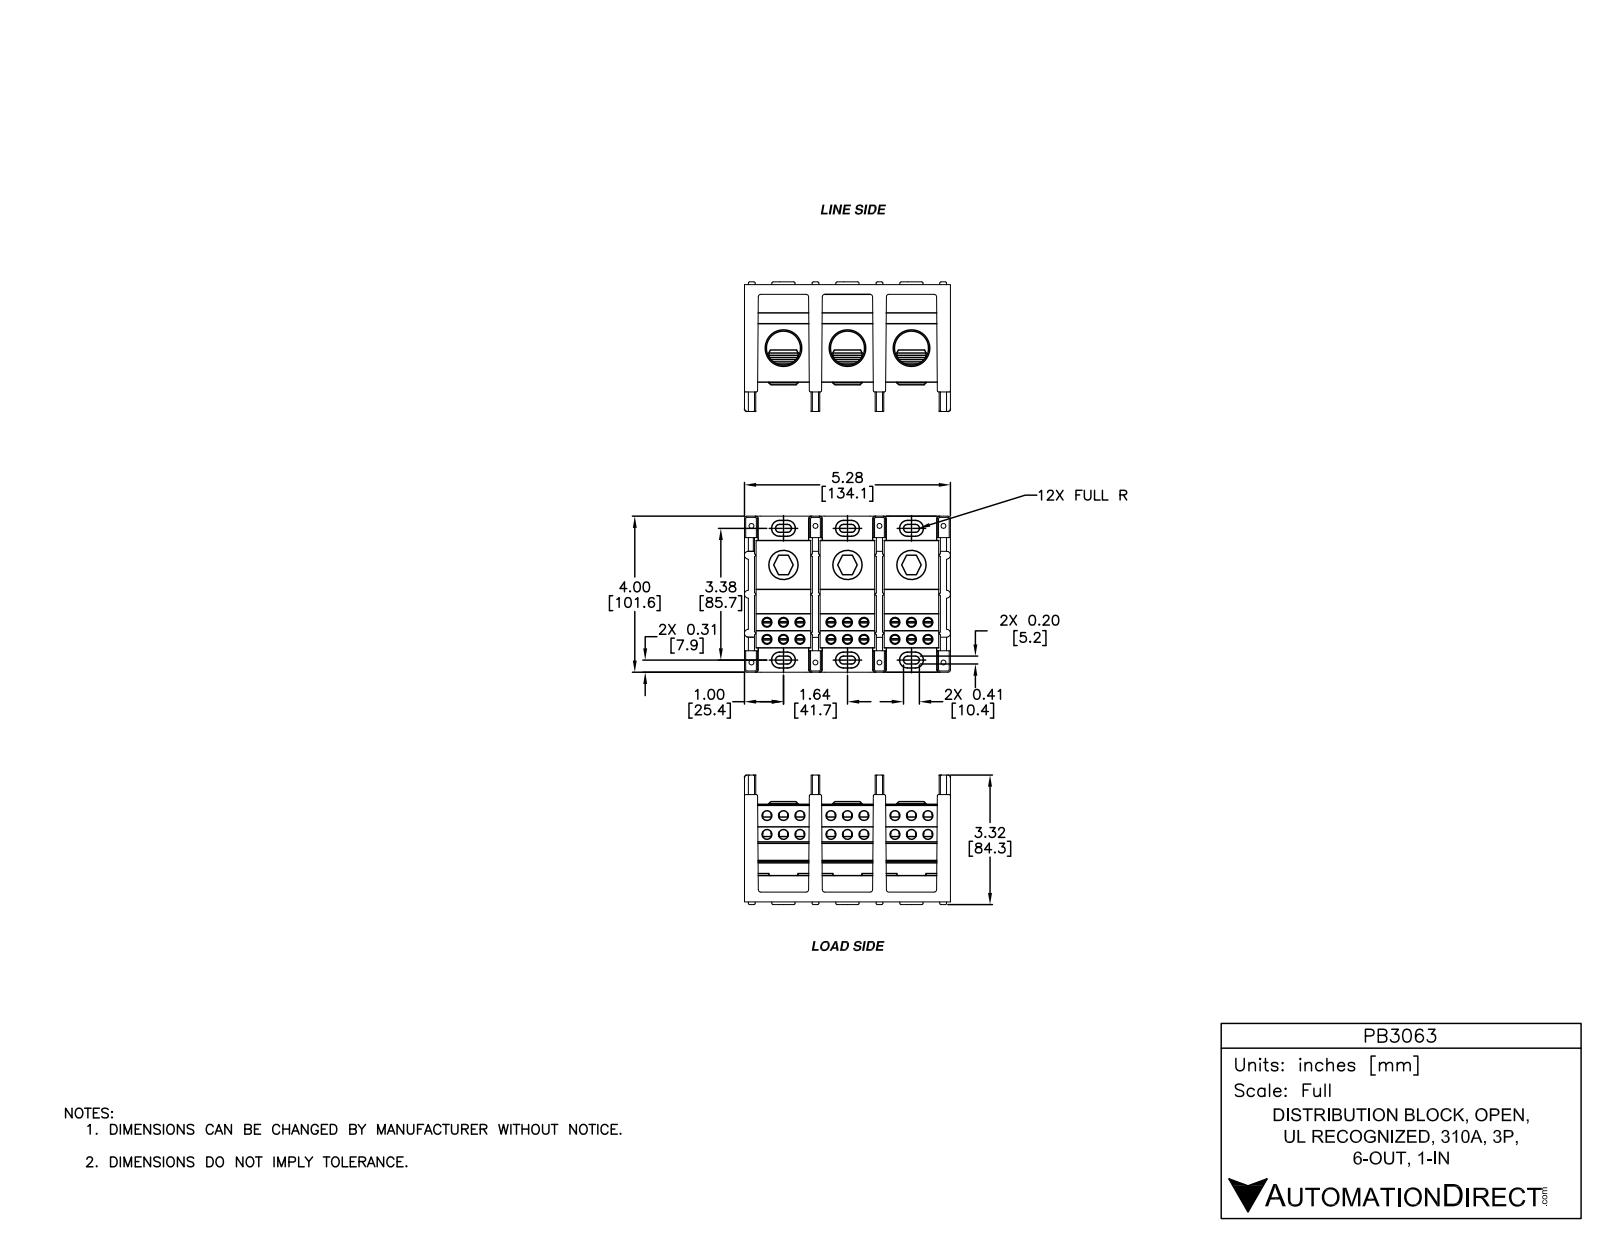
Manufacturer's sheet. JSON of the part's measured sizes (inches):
{"part_name": "PB3063", "step_written_by": "SolidWorks 2014 (AUTOMOTIVE_DESIGN)", "units": "inches", "bodies": {"solids": 10, "faces": 1420, "planar": 570, "cylindrical": 581, "other": 269}, "overall_size": [5.281, 4, 3.35], "volume_in3": 26.9, "surface_area_in2": 276.7, "round_holes": [[0.219, 18], [0.25, 18], [0.125, 8], [0.75, 4], [0.5, 3], [0.875, 3]], "round_bosses_or_shafts": [[0.174, 8], [0.062, 7], [0.375, 3]], "partial_cylinders_radius": [[0.031, 79], [0.1, 54], [0.063, 37], [0.203, 24], [0.062, 20], [0.094, 12]], "face_to_face_distances": [1.641, 3.281, 0.159, 1.481, 1.8, 0.1, 3.122, 0.75, 0.35, 3.441], "hole_center_spacings": [1.641, 0.422, 3.282, 1.219, 2.063, 0.641, 0.845, 1.71]}
